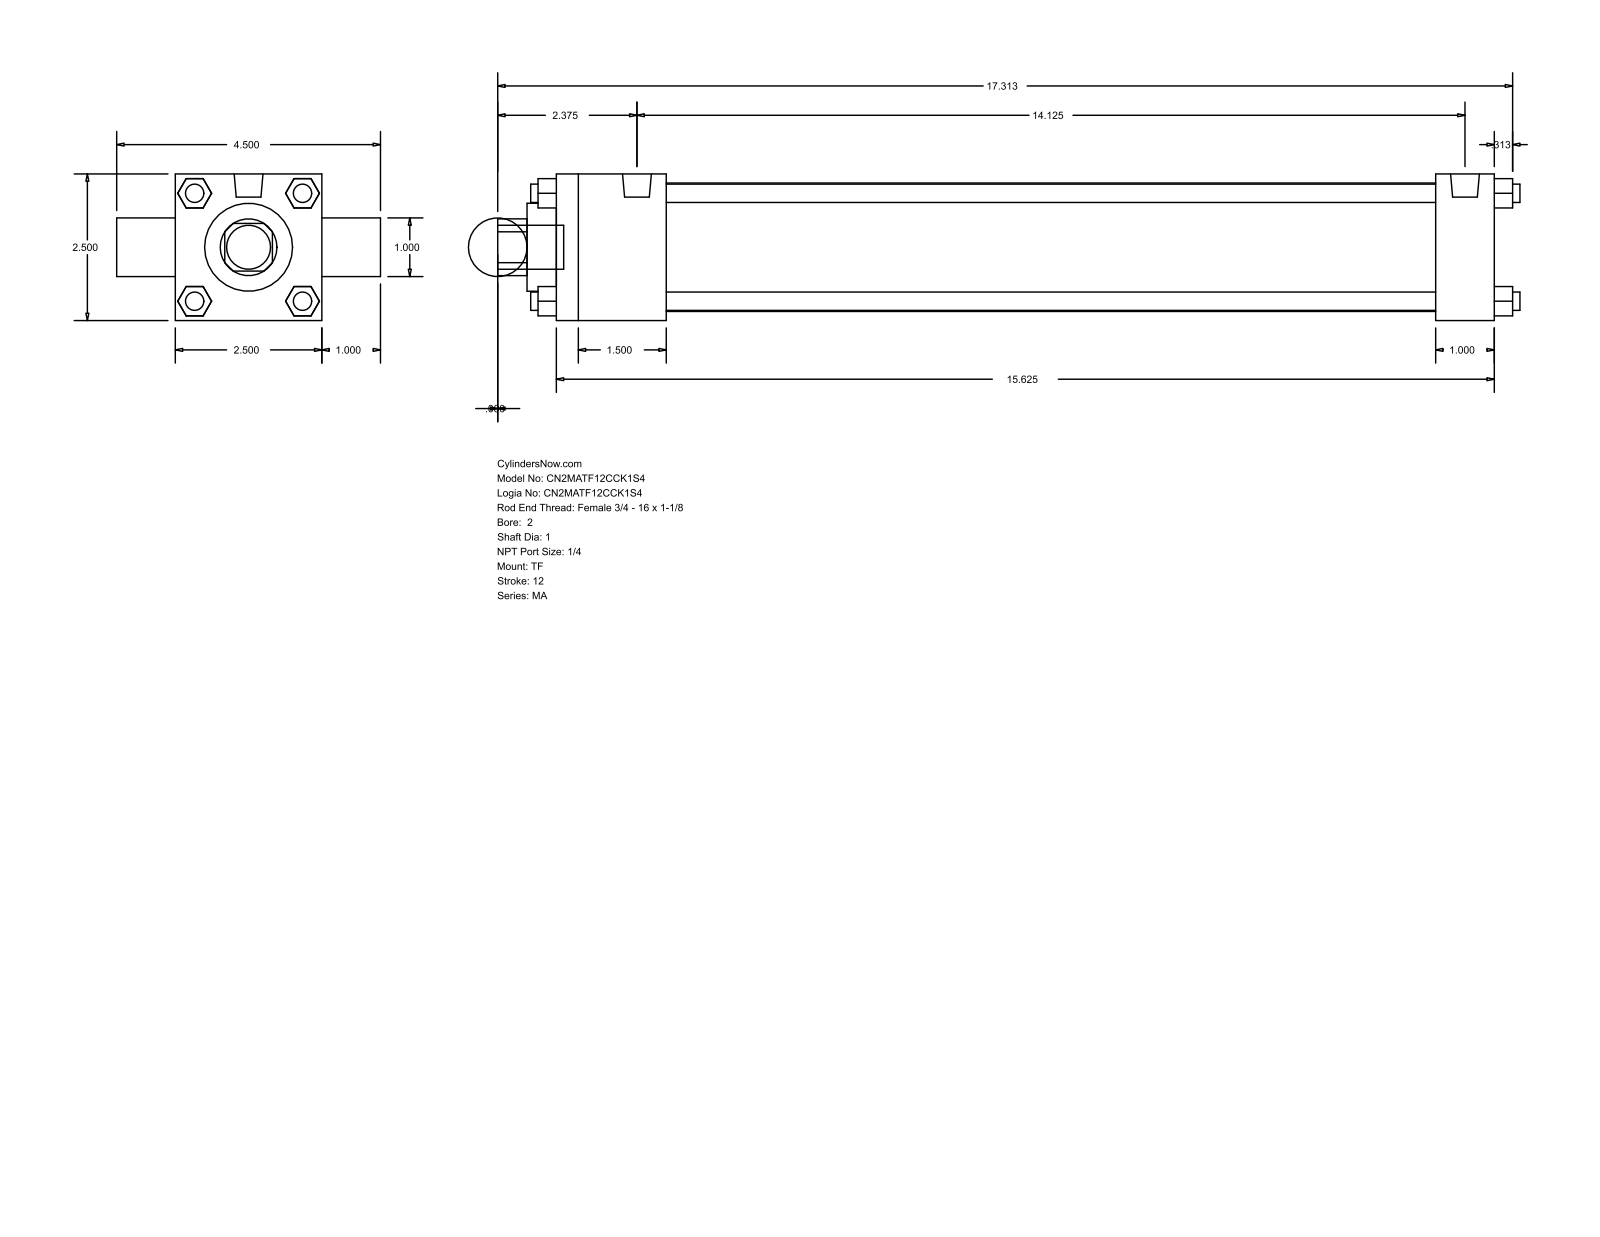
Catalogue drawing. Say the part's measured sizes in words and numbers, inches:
The part is named "MA_TF__0200_1". Its 3-D file was written by "GSSL Pune (CONFIG_CONTROL_DESIGN)". It is 0 solids with 120 faces: 92 planar, 28 cylindrical and 0 other. Overall it measures 17.437 by 4.5 by 2.5 inches. Round holes: 2 of diameter 1, 1 of diameter 1.5, 1 of diameter 2.19. Round bosses or shafts: 7 of diameter 0.313, 2 of diameter 0.492, 1 of diameter 0.75. Partial cylindrical surfaces (rounded edges, fillets, slot ends): 1 of radius 0.484. The main face-to-face distances are 2.5, 1, 16, 0.5, 1.875, 15, 13.125, 14.125, 3.5, 1.593.
